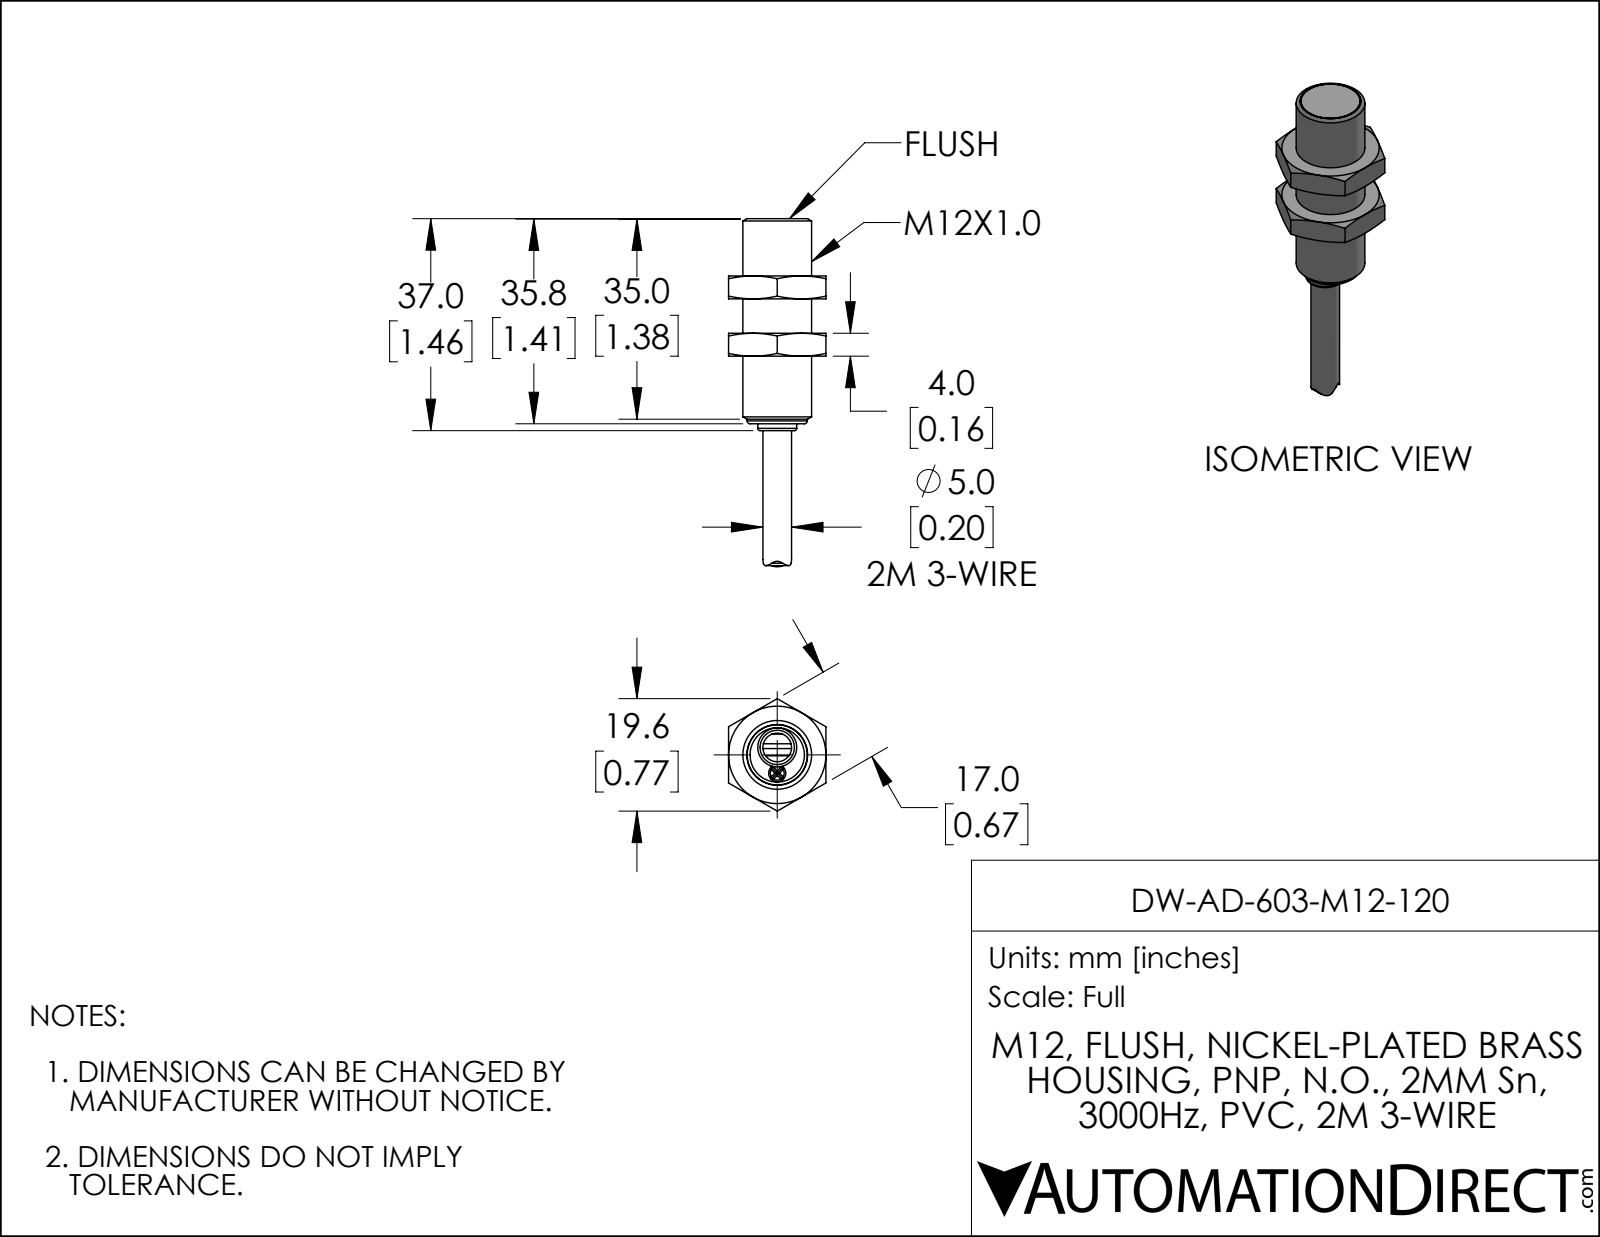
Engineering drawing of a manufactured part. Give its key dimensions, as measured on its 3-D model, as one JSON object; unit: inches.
{"part_name": "DW-AD-603-M12-120", "step_written_by": "SolidWorks 2019 (AUTOMOTIVE_DESIGN)", "units": "inches", "bodies": {"solids": 1, "faces": 81, "planar": 34, "cylindrical": 14, "other": 33}, "overall_size": [2.392, 0.773, 0.669], "volume_in3": 0.342, "surface_area_in2": 4.072, "round_holes": [[0.415, 1]], "round_bosses_or_shafts": [[0.472, 1], [0.413, 1], [0.406, 1], [0.268, 1], [0.197, 1], [0.118, 1]], "partial_cylinders_radius": [[0.031, 1], [0.041, 1], [0.165, 1], [0.248, 1], [0.331, 1]], "face_to_face_distances": [0.394, 0.157, 0.669, 0.551, 0.236, 0.787, 0.945, 1.409, 1.016, 0.858]}
